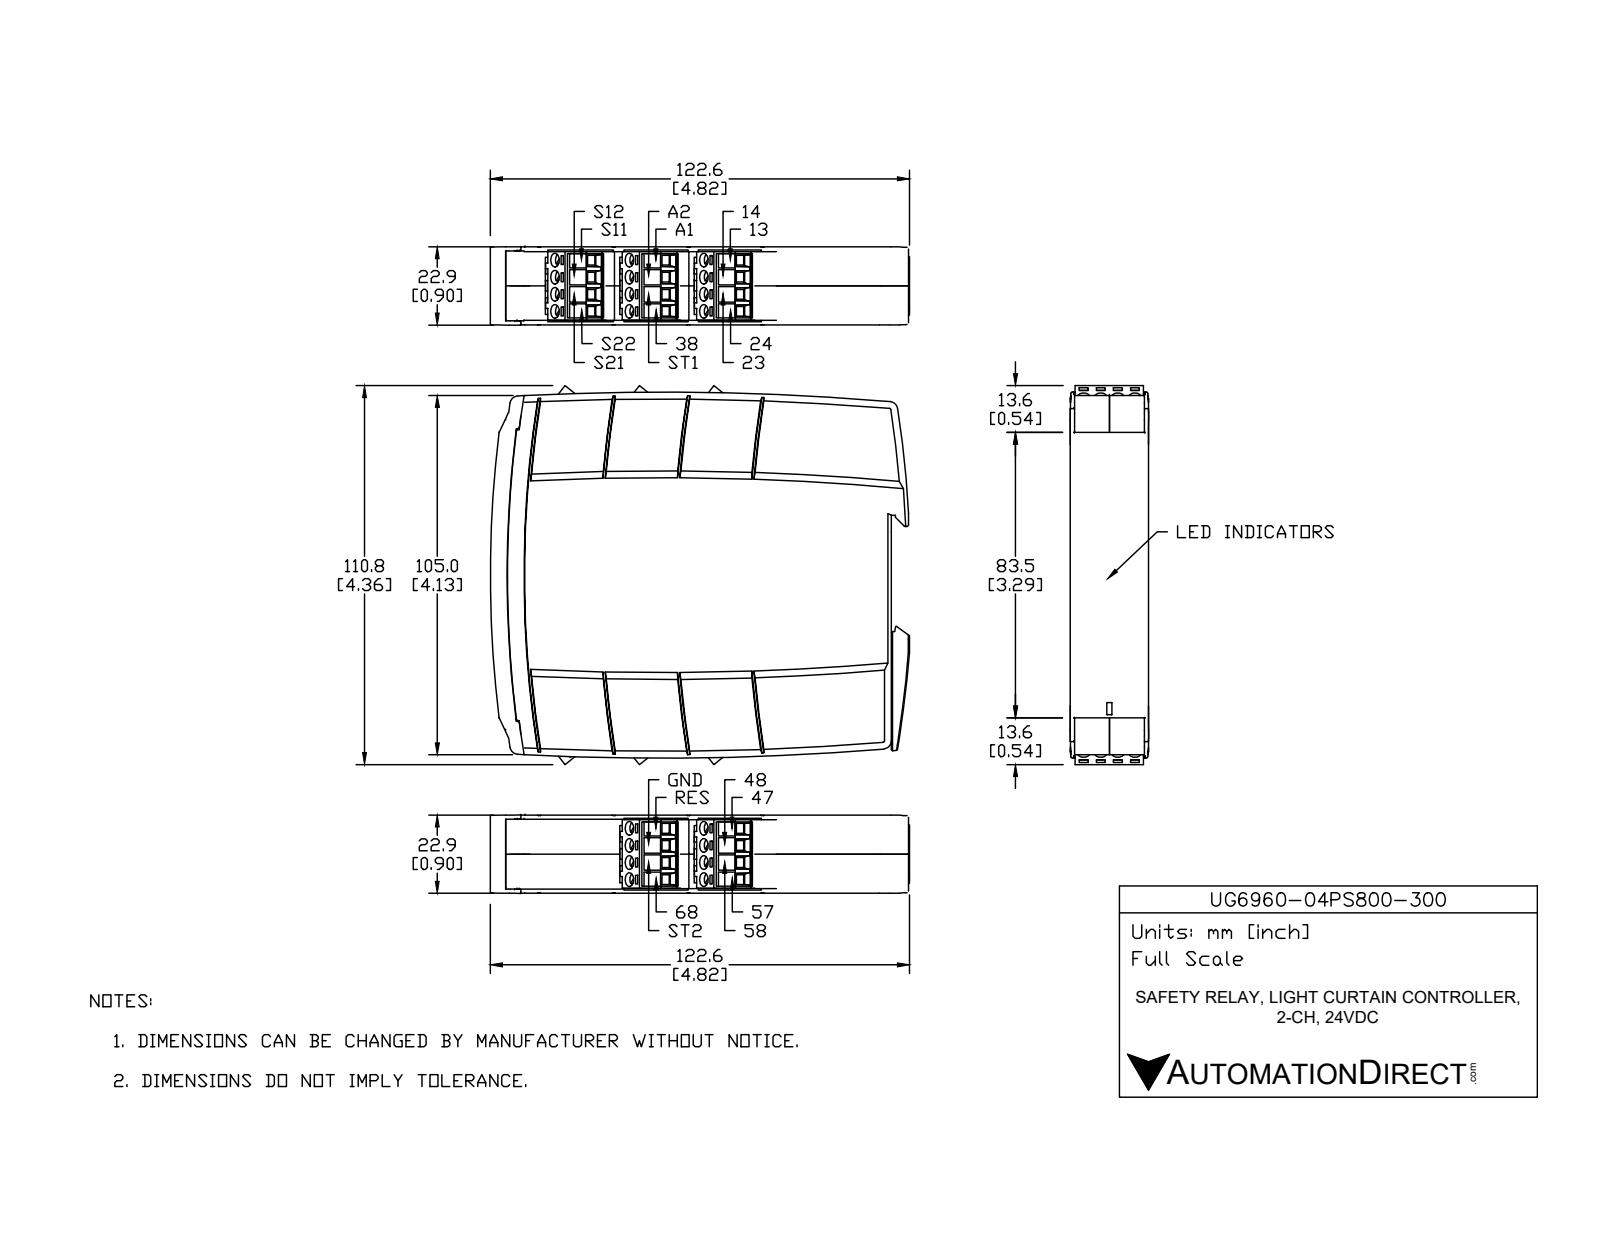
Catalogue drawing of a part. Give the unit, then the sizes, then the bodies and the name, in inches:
Units: inches
Overall size (bounding box): 4.813 × 4.355 × 0.886
Round holes (diameter × count): ⌀0.157 ×20
Partial cylindrical surfaces — rounded edges, fillets, slot ends (radius × count): R0.012 ×12, R0.094 ×7, R0.02 ×2, R31.496 ×2
Main face-to-face distances: 0.886, 0.675, 0.528, 0.049, 0.837, 1.35, 0.787, 0.567, 0.591, 0.528
Hole centre spacings: 0.197, 0.563, 0.394, 0.528, 0.658, 0.563, 1.074, 0.591
Volume: 16.61 in³ · Surface area: 60.34 in²
Bodies: 1 solid, 501 faces (447 planar, 45 cylindrical, 9 other)
Part name (STEP PRODUCT): UG6960-04PS800-300
STEP written by: SolidWorks 2021 (AUTOMOTIVE_DESIGN)
